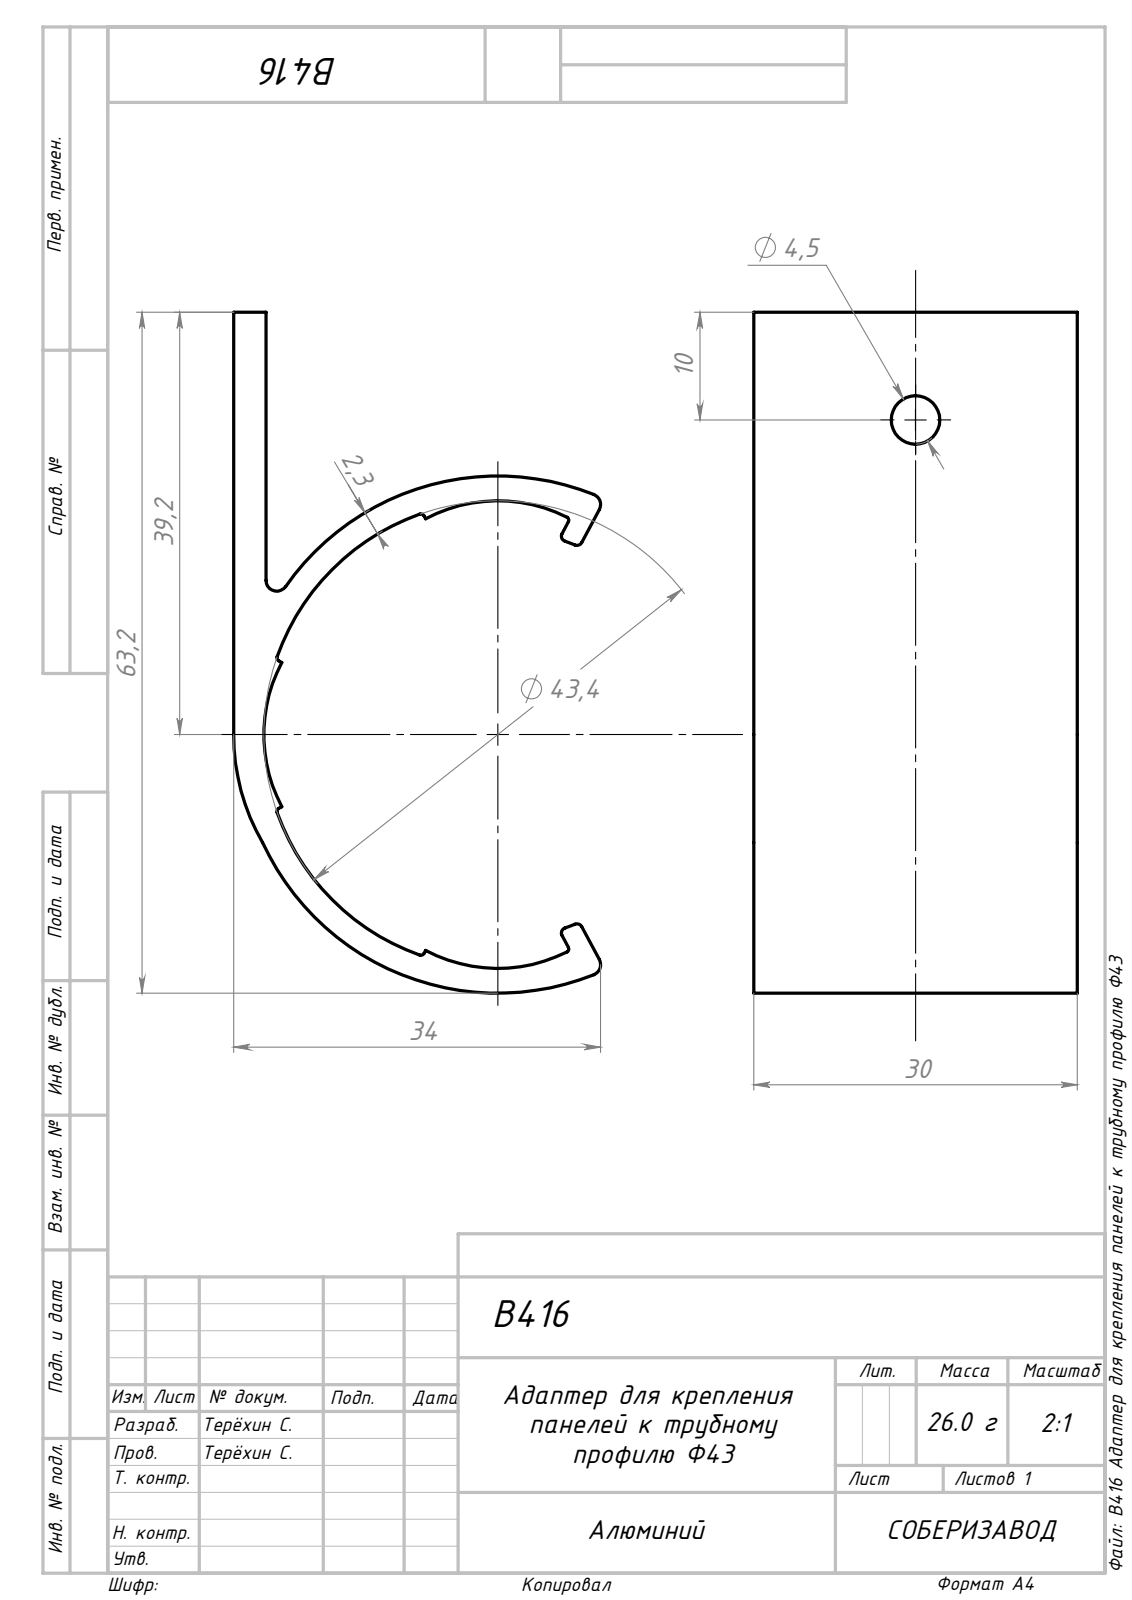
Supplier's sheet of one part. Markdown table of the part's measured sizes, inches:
| quantity | value |
| --- | --- |
| part name | B416 Адаптер для крепления панелей к трубному профилю Ф43 |
| STEP written by | SolidWorks 2022 (AUTOMOTIVE_DESIGN) |
| units | inches |
| bodies | 1 solid, 43 faces (13 planar, 27 cylindrical, 3 other) |
| overall size | 2.488 × 1.34 × 1.181 |
| volume | 0.606 in³ |
| surface area | 12.69 in² |
| round holes (diameter × count) | 0.177 × 1 |
| partial cylindrical surfaces (radius × count) | 0.012 × 6, 0.02 × 4, 0.039 × 3, 0.559 × 3, 0.748 × 1, 0.787 × 1, 0.854 × 1, 0.945 × 1 |
| main face-to-face distances | 0.118, 1.181, 0.079, 0.278, 0.199 |
